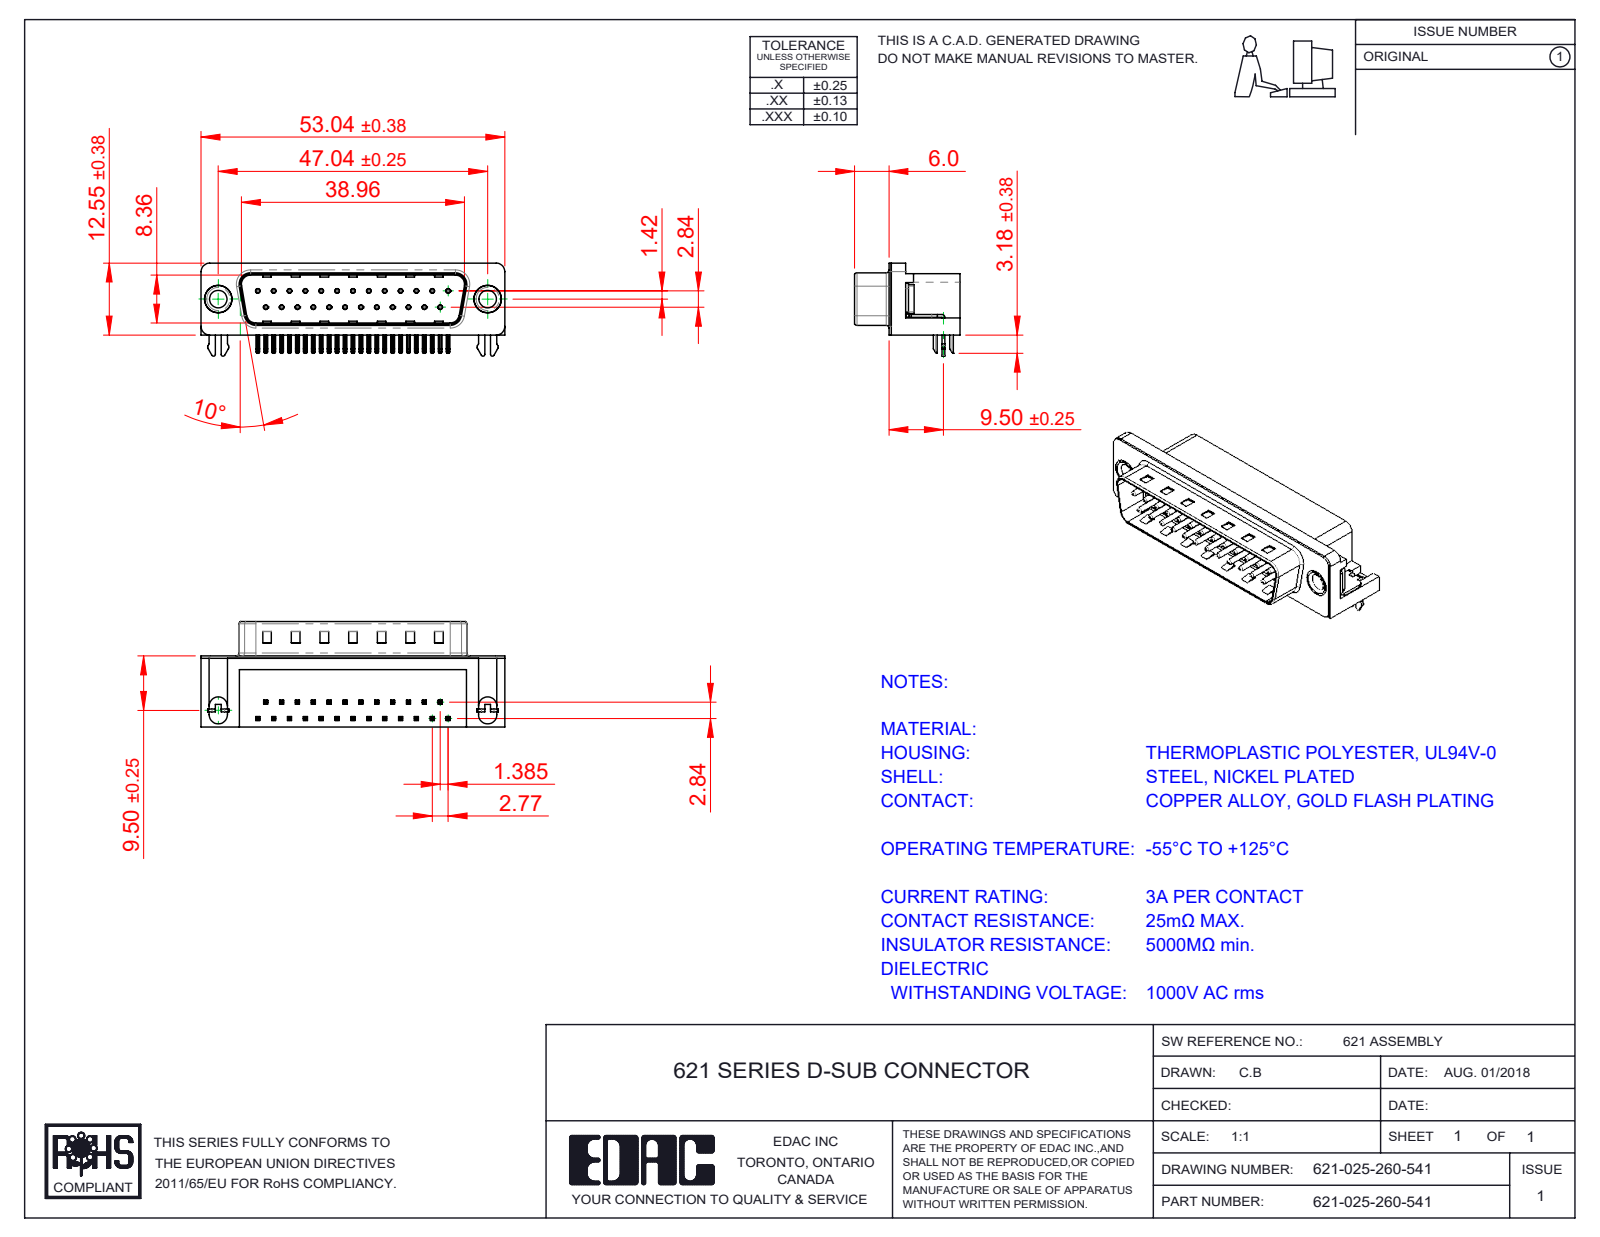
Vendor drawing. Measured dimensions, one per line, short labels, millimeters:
name: 621 Contact Top; 621 Contact Bottom; 621-025-260-541; 621 Shell_25 Socket (+3 more)
written by: SolidWorks 2016 (CONFIG_CONTROL_DESIGN)
unit: mm
bodies: 31 solids, 2343 faces (1447 planar, 647 cylindrical, 249 other)
size: 53.04 × 18.4 × 16.25
volume: 6 345 mm³; area: 7 734 mm²
holes: 25× ⌀0.35, 25× ⌀0.8, 2× ⌀2, 2× ⌀3.05, 2× ⌀4, 2× ⌀4.8, 2× ⌀5
bosses: 25× ⌀0.75, 2× ⌀4.9, 2× ⌀4.75, 2× ⌀3.85, 2× ⌀3
rounds: 112× R0.25, 50× R0.12, 16× R1, 9× R0.5, 8× R1.6, 7× R1.5, 4× R0.9, 4× R2
face distances: 0.4, 12, 10.35, 2.1, 8.76, 10.46, 1.7, 10.86, 12.4, 9
hole spacings: 3.16, 2.77, 5.54, 8.31, 11.08, 13.85, 16.62, 5.03
